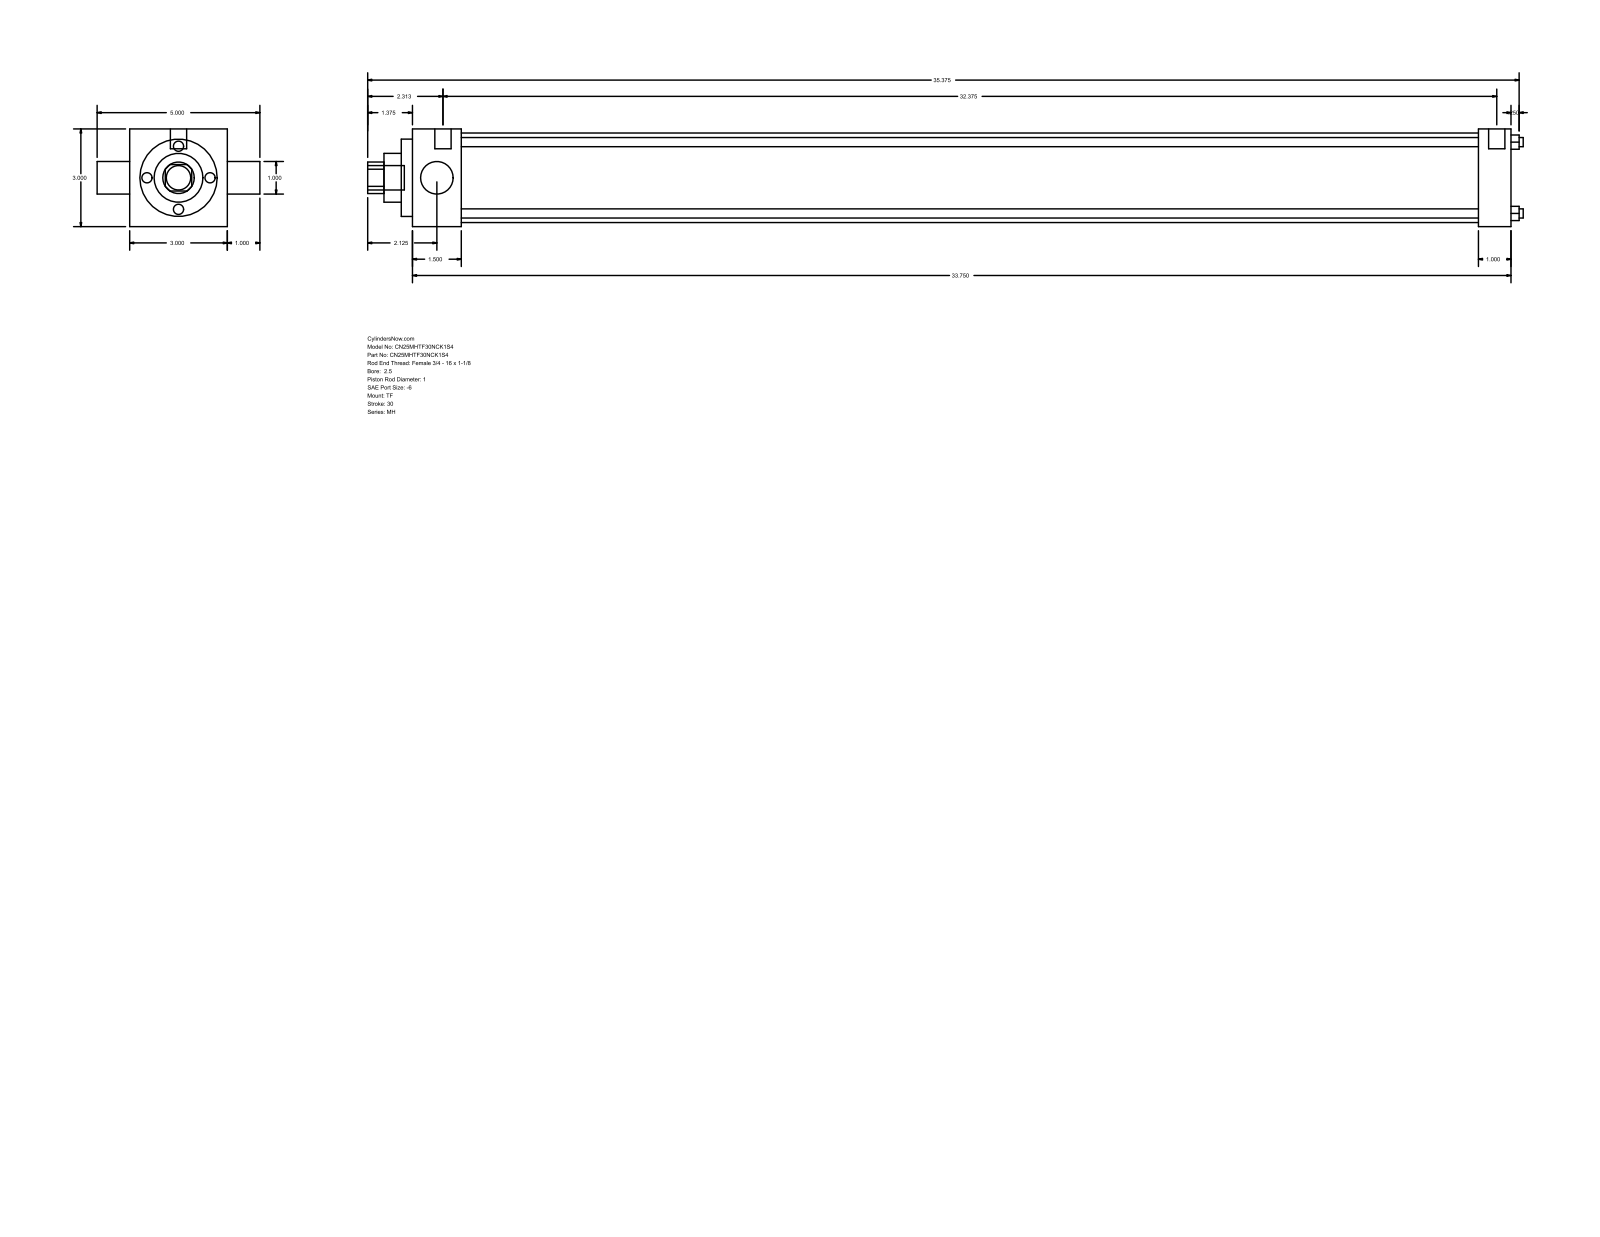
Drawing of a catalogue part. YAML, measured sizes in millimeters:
part_name: "MH_TF__0250_1"
step_written_by: "GSSL Pune (CONFIG_CONTROL_DESIGN)"
units: millimeters
bodies: {solids: 0, faces: 86, planar: 61, cylindrical: 25, other: 0}
overall_size: [901.7, 127, 76.2]
round_holes:
  - {diameter: 7.14, count: 4}
  - {diameter: 25.4, count: 2}
  - {diameter: 38.1, count: 1}
  - {diameter: 60.33, count: 1}
  - {diameter: 69.85, count: 1}
round_bosses_or_shafts:
  - {diameter: 5.56, count: 3}
  - {diameter: 12.7, count: 2}
  - {diameter: 19.05, count: 1}
partial_cylinders:
  - {radius: 12.29, count: 1}
face_to_face_distances: [76.2, 857.25, 25.4, 38.11, 819.14, 831.85, 793.74, 8.73, 46.84, 840.58]
hole_center_spacings: [39.33, 55.62, 78.66]
